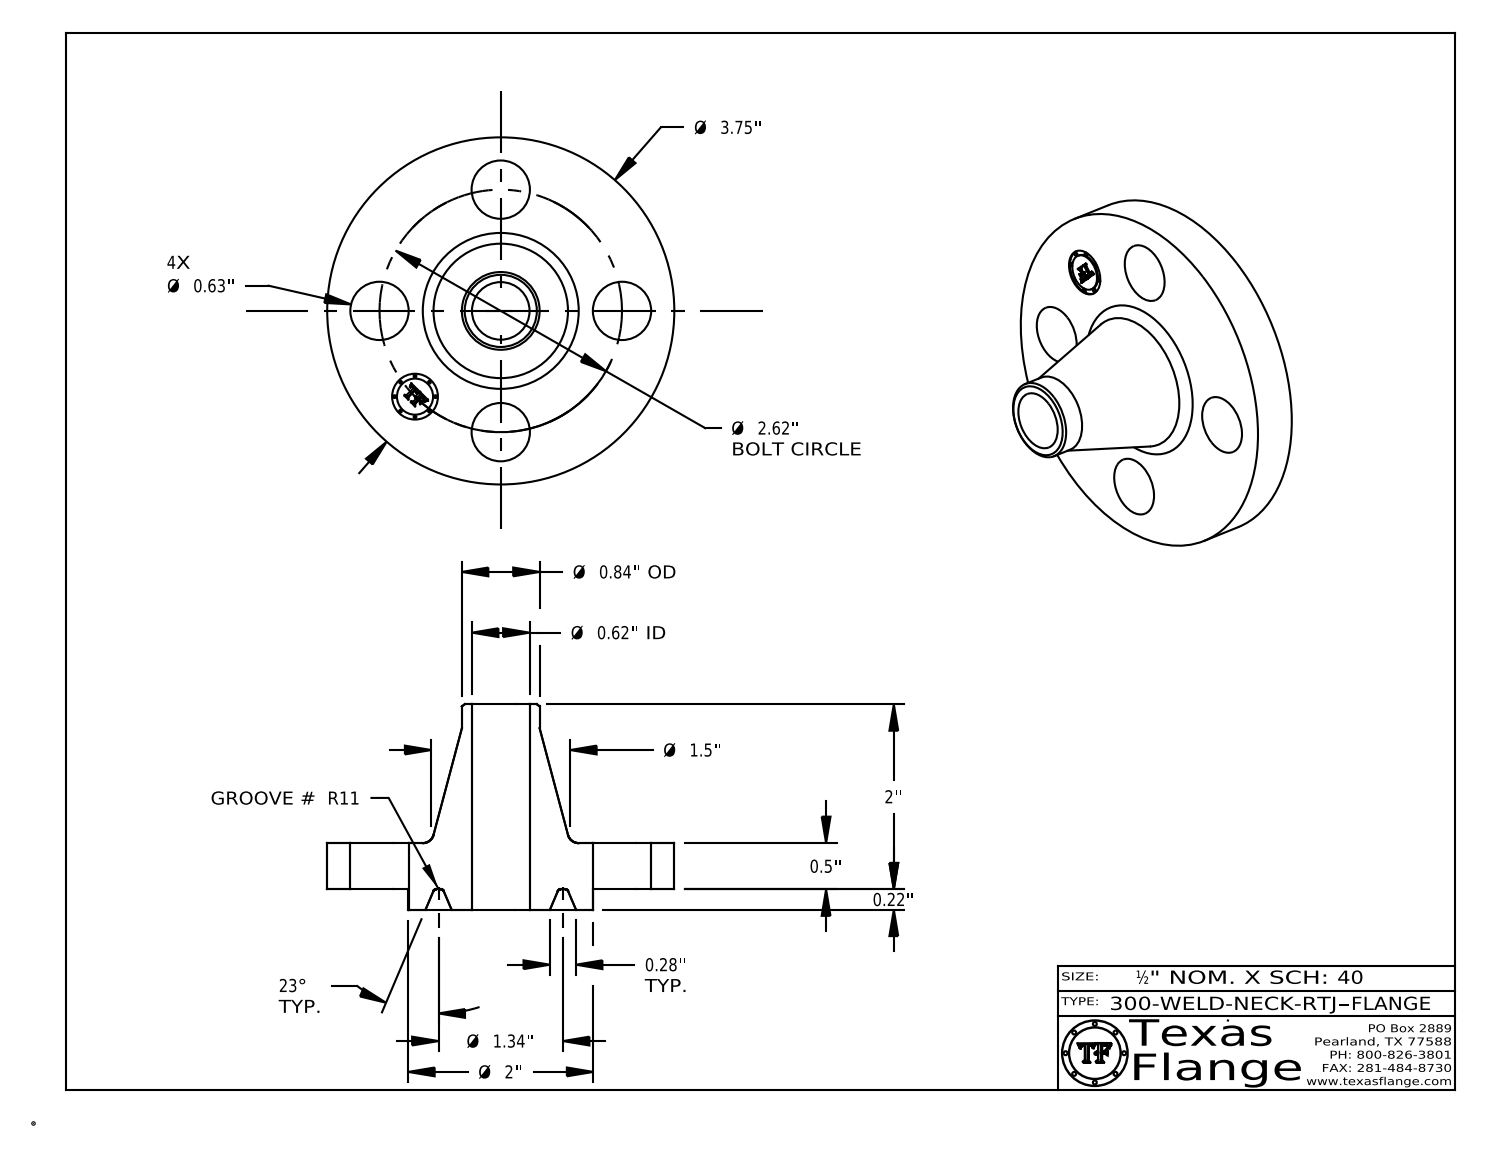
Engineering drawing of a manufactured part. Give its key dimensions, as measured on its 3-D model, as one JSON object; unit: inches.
{"part_name": "300-WELD-NECK-RTJ", "step_written_by": "CATIA V5 STEP AP214 (AUTOMOTIVE_DESIGN)", "units": "inches", "bodies": {"solids": 1, "faces": 425, "planar": 371, "cylindrical": 40, "other": 14}, "overall_size": [3.75, 3.75, 2.219], "volume_in3": 6.258, "surface_area_in2": 39.85, "round_holes": [[0.63, 4], [0.495, 1], [0.622, 1]], "round_bosses_or_shafts": [[0.03, 8], [3.75, 1], [2, 1], [0.84, 1], [0.39, 1]], "face_to_face_distances": [0.5, 0.219, 0.719, 2.219, 2, 1.5, 0.704, 0.485, 0.015, 1.515], "hole_center_spacings": [1.31, 1.852, 1.003, 2.42, 2.62, 1.31]}
